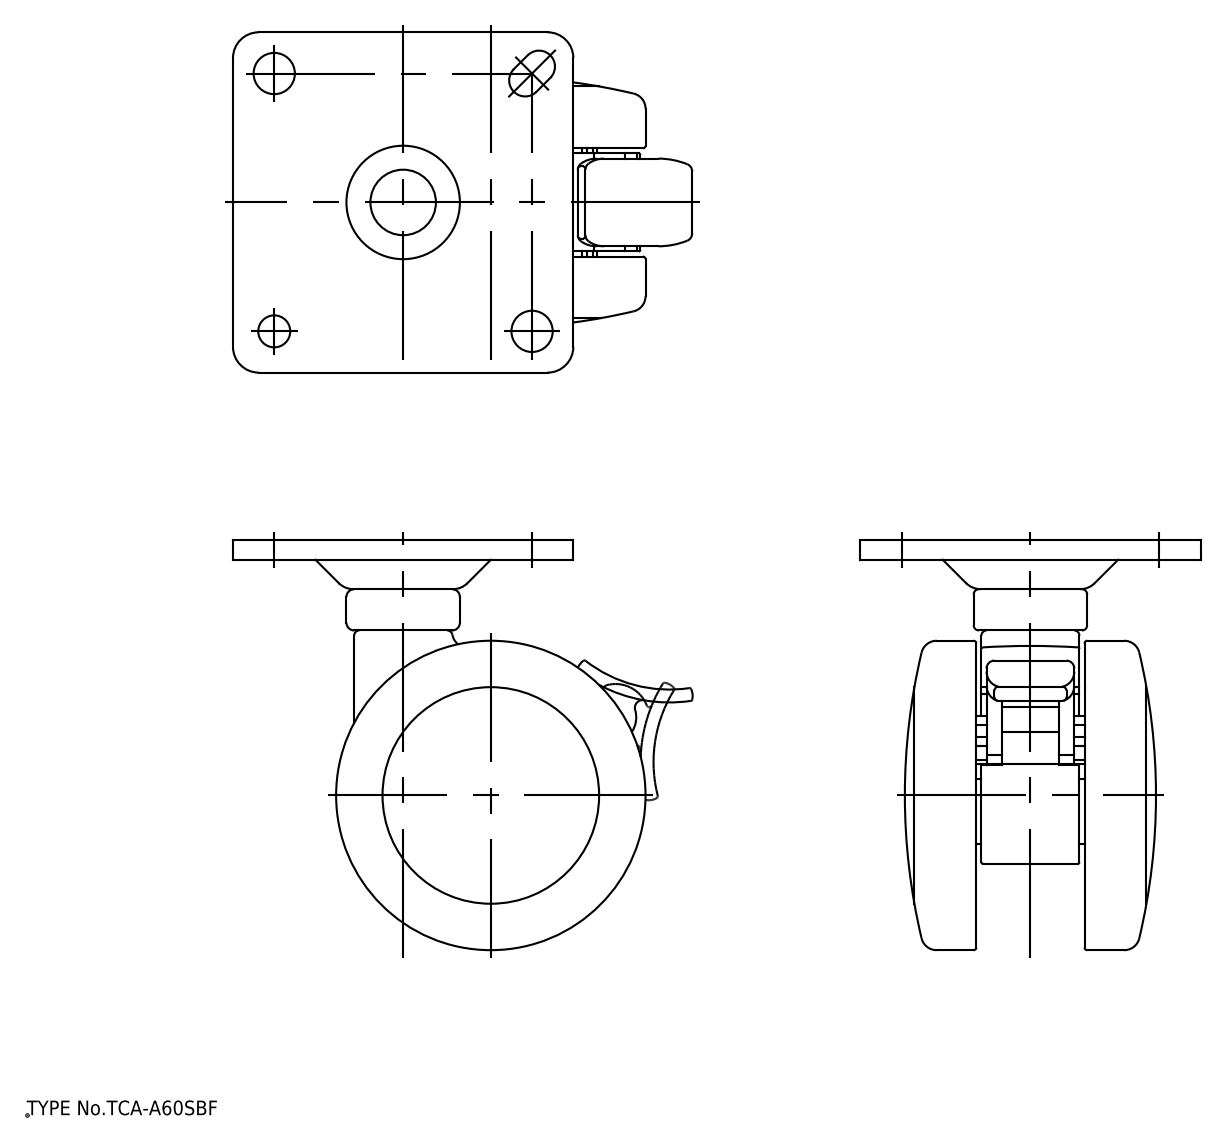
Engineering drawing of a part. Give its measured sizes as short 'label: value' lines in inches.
name: A60S _{; TY60JS ___o_[; A60; TY75 ___t
written by: spGate 18.9.1 (****-****-****-****) (AUTOMOTIVE_DESIGN)
unit: in
bodies: 5 solids, 268 faces (51 planar, 91 cylindrical, 126 other)
size: 3.516 × 3.13 × 2.598
volume: 6.82 in³; area: 75.04 in²
holes: 2× ⌀0.315, 1× ⌀0.142, 1× ⌀0.244, 1× ⌀0.358, 1× ⌀0.472, 1× ⌀0.846, 1× ⌀0.984, 1× ⌀1.713, 1× ⌀1.732
bosses: 1× ⌀2.362, 1× ⌀1.654, 1× ⌀0.866, 1× ⌀0.748, 1× ⌀0.433, 1× ⌀0.354, 1× ⌀0.157, 1× ⌀0.138
rounds: 5× R0.012, 5× R0.059, 5× R0.197, 2× R0.122, 2× R0.591, 2× R3.926, 1× R0.02, 1× R0.138
face distances: 1.22, 0.039, 0.433, 0.236, 0.197, 0.472, 0.15, 1.26, 0.787, 1.024
hole spacings: 1.392, 1.969, 1.083, 2.784
